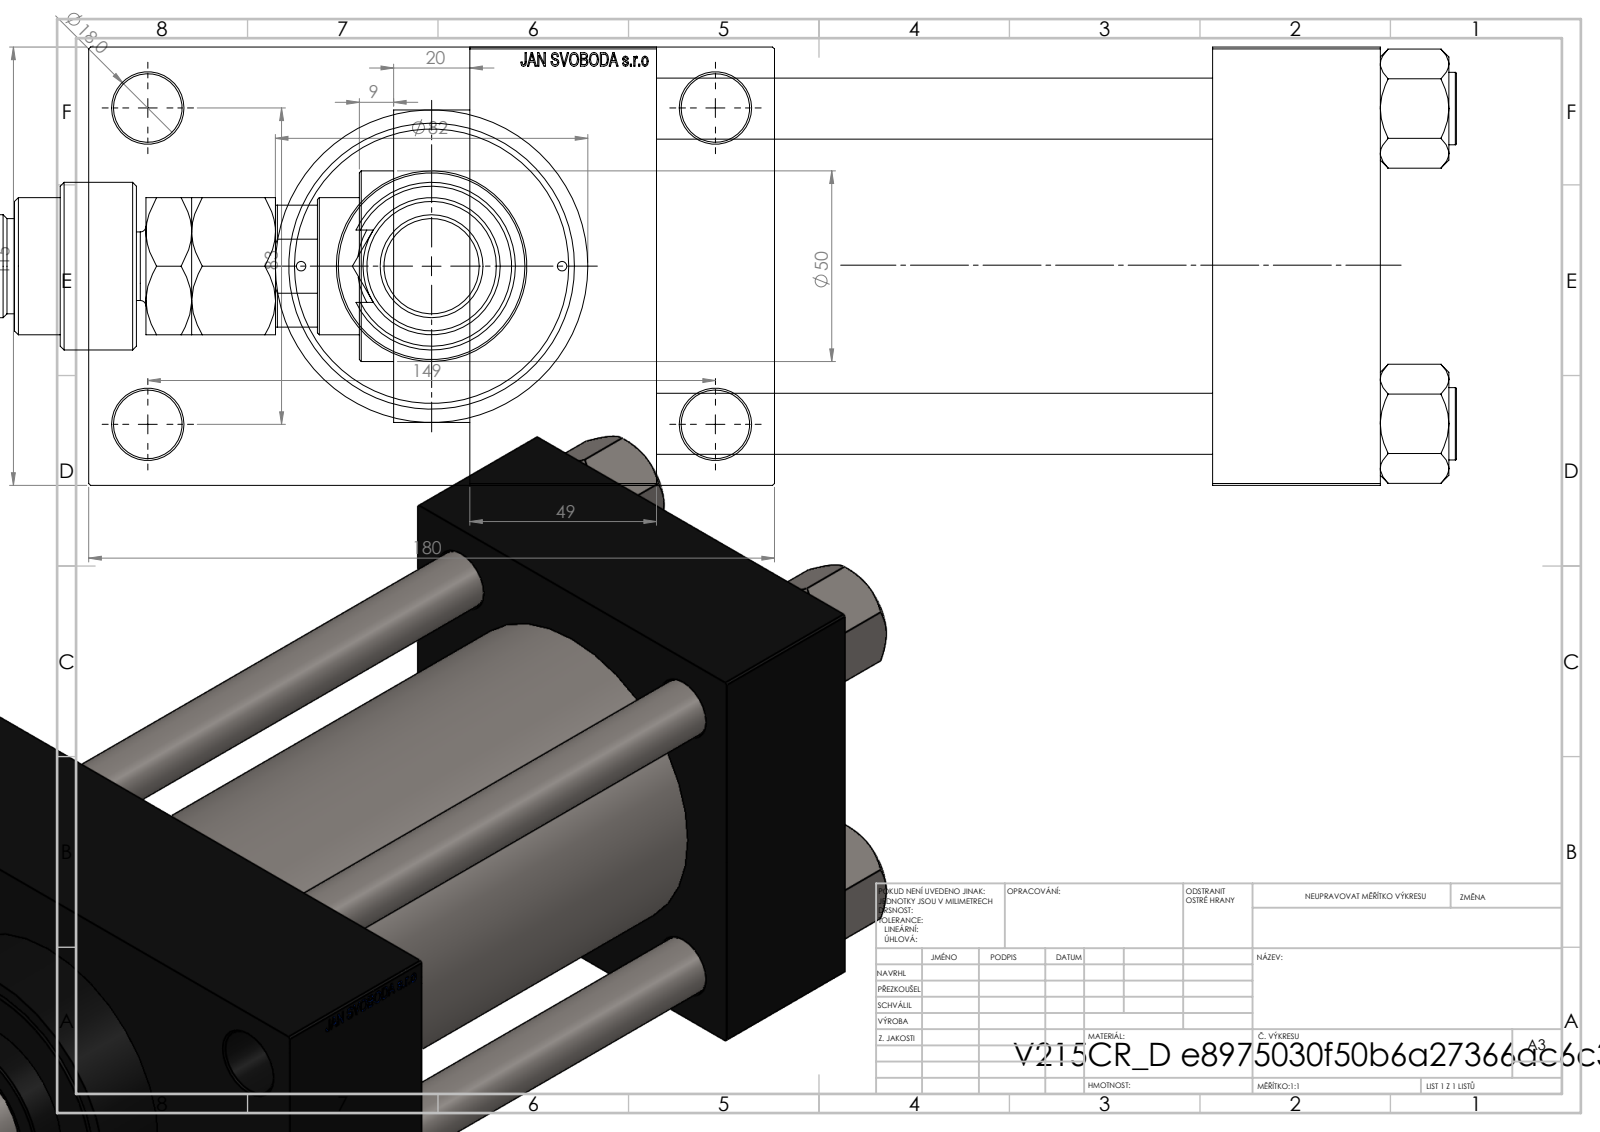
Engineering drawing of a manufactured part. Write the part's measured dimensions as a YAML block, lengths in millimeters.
part_name: "V215CR_VCP_D; V215_VC_A; FEMALE_PART_FOR_DFA; V215CR_D_Body (+3 more)"
step_written_by: "SolidWorks 2019 (CONFIG_CONTROL_DESIGN)"
units: millimeters
bodies: {solids: 13, faces: 1244, planar: 575, cylindrical: 105, other: 564}
overall_size: [420.5, 180, 115]
volume: 2286000
surface_area: 384449
round_holes:
  - {diameter: 16, count: 4}
  - {diameter: 18, count: 4}
  - {diameter: 2.5, count: 2}
  - {diameter: 7, count: 2}
  - {diameter: 26.44, count: 2}
  - {diameter: 35, count: 2}
  - {diameter: 25.5, count: 1}
  - {diameter: 39, count: 1}
  - {diameter: 61, count: 1}
  - {diameter: 72, count: 1}
  - {diameter: 80, count: 1}
round_bosses_or_shafts:
  - {diameter: 19, count: 4}
  - {diameter: 86, count: 1}
  - {diameter: 82, count: 1}
  - {diameter: 50, count: 1}
  - {diameter: 44, count: 1}
  - {diameter: 36, count: 1}
  - {diameter: 28, count: 1}
  - {diameter: 27, count: 1}
partial_cylinders:
  - {radius: 9.5, count: 1}
  - {radius: 15, count: 1}
  - {radius: 17.5, count: 1}
face_to_face_distances: [115, 146, 195, 49, 44, 190, 239, 32.5, 147.5, 100]
hole_center_spacings: [33.15, 41.96, 57.81, 58.48, 82.7, 85.28, 86.17, 89.24]
